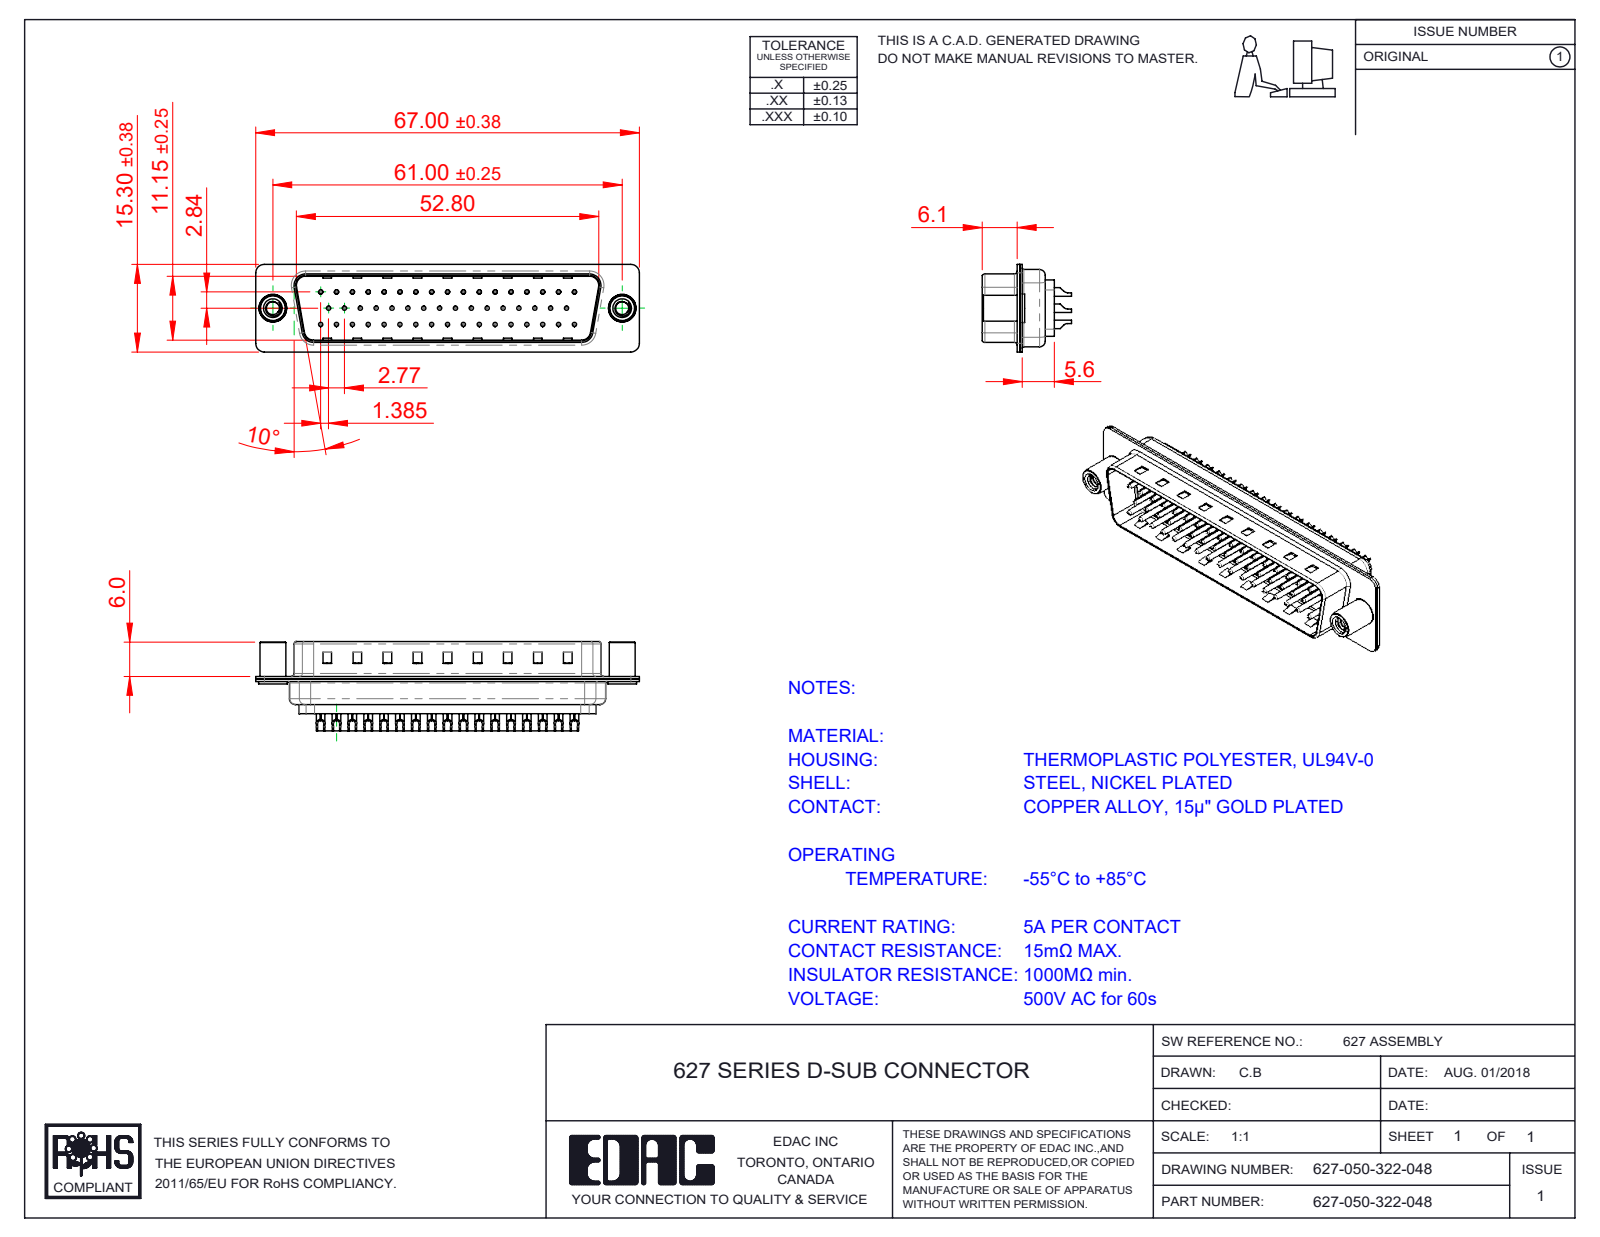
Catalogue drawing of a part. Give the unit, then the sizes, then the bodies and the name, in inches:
Units: inches
Overall size (bounding box): 2.638 × 0.614 × 0.602
Round holes (diameter × count): ⌀0.063 ×58, ⌀0.014 ×50, ⌀0.043 ×50, ⌀0.03 ×8, ⌀0.079 ×8, ⌀0.089 ×2, ⌀0.157 ×2, ⌀0.189 ×2
Round bosses / shafts (diameter × count): ⌀0.079 ×50, ⌀0.059 ×50, ⌀0.03 ×50, ⌀0.197 ×2, ⌀0.193 ×2, ⌀0.177 ×2
Partial cylindrical surfaces — rounded edges, fillets, slot ends (radius × count): R0.059 ×16, R0.079 ×12, R0.02 ×8, R0.063 ×8, R0.039 ×7, R0.01 ×4, R0.024 ×4, R0.026 ×4
Main face-to-face distances: 0.016, 0.018, 0.455, 0.035, 0.238, 0.256, 0.031, 0.077, 0.03, 0.485
Hole centre spacings: 0.109, 0.124, 0.218, 0.327, 0.436, 0.545, 0.654, 0.763
Volume: 0.276 in³ · Surface area: 20.1 in²
Bodies: 55 solids, 3646 faces (905 planar, 1619 cylindrical, 1122 other)
Part name (STEP PRODUCT): 627 Contact Row 2_22M; 627 4-40 Threaded Standoff; 627 Shell Front_50 Contacts; 627-050-322-048 (+4 more)
STEP written by: SolidWorks 2020 (CONFIG_CONTROL_DESIGN)
